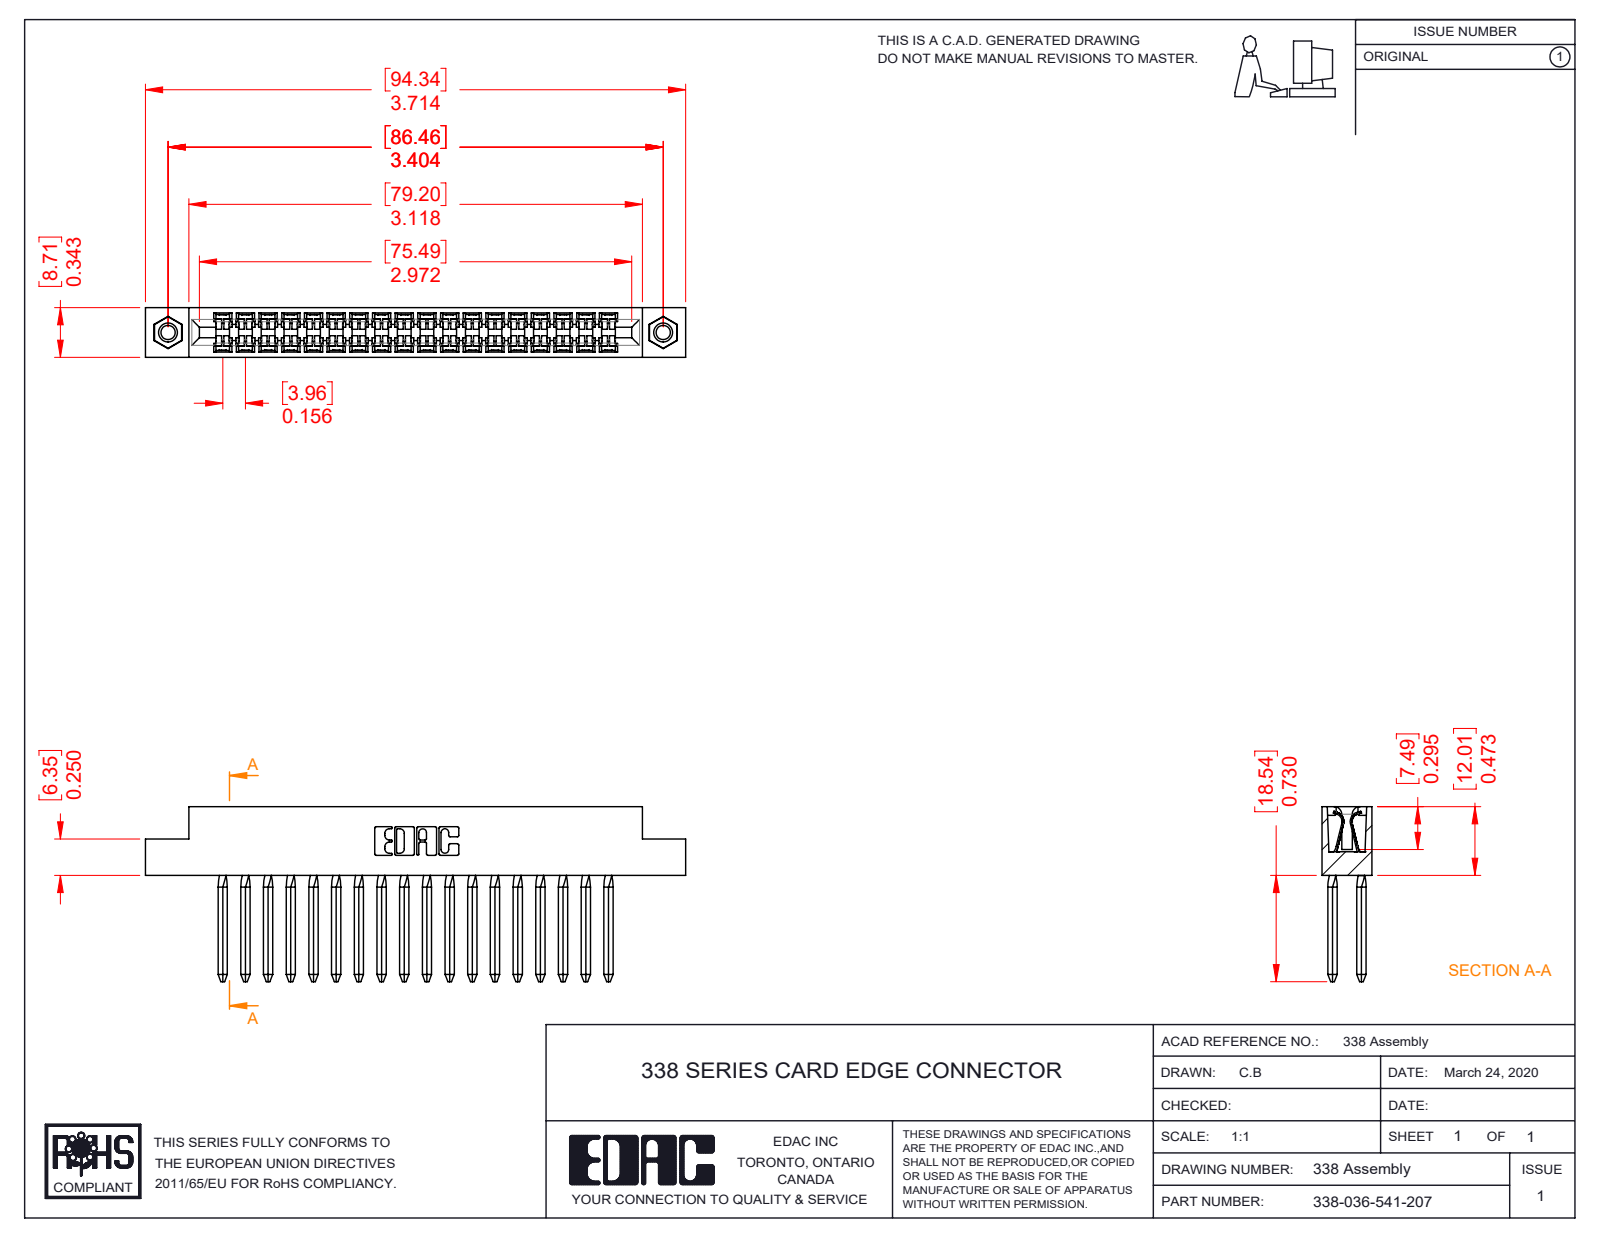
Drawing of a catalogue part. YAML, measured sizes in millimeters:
part_name: "338-210-001_338-210-018-004; 338-036-541-207; 345-250-001_345-250-005-103; 338-290-001_541"
step_written_by: "SolidWorks 2016 (CONFIG_CONTROL_DESIGN)"
units: millimeters
bodies: {solids: 39, faces: 2566, planar: 1774, cylindrical: 632, other: 160}
overall_size: [94.3, 30.6, 8.7]
volume: 7190
surface_area: 13100
round_holes:
  - {diameter: 2.5, count: 2}
  - {diameter: 3.2, count: 2}
  - {diameter: 4, count: 2}
round_bosses_or_shafts:
  - {diameter: 3.9, count: 2}
partial_cylinders:
  - {radius: 0.6, count: 110}
  - {radius: 0.2, count: 36}
  - {radius: 1.4, count: 30}
  - {radius: 1.7, count: 30}
  - {radius: 2.5, count: 28}
  - {radius: 0.3, count: 22}
  - {radius: 0.2, count: 6}
  - {radius: 0.8, count: 6}
face_to_face_distances: [8.7, 4, 15.8, 2.8, 19.8, 11.9, 3.4, 5.3, 5.6, 7.9]
hole_center_spacings: [86.5]
